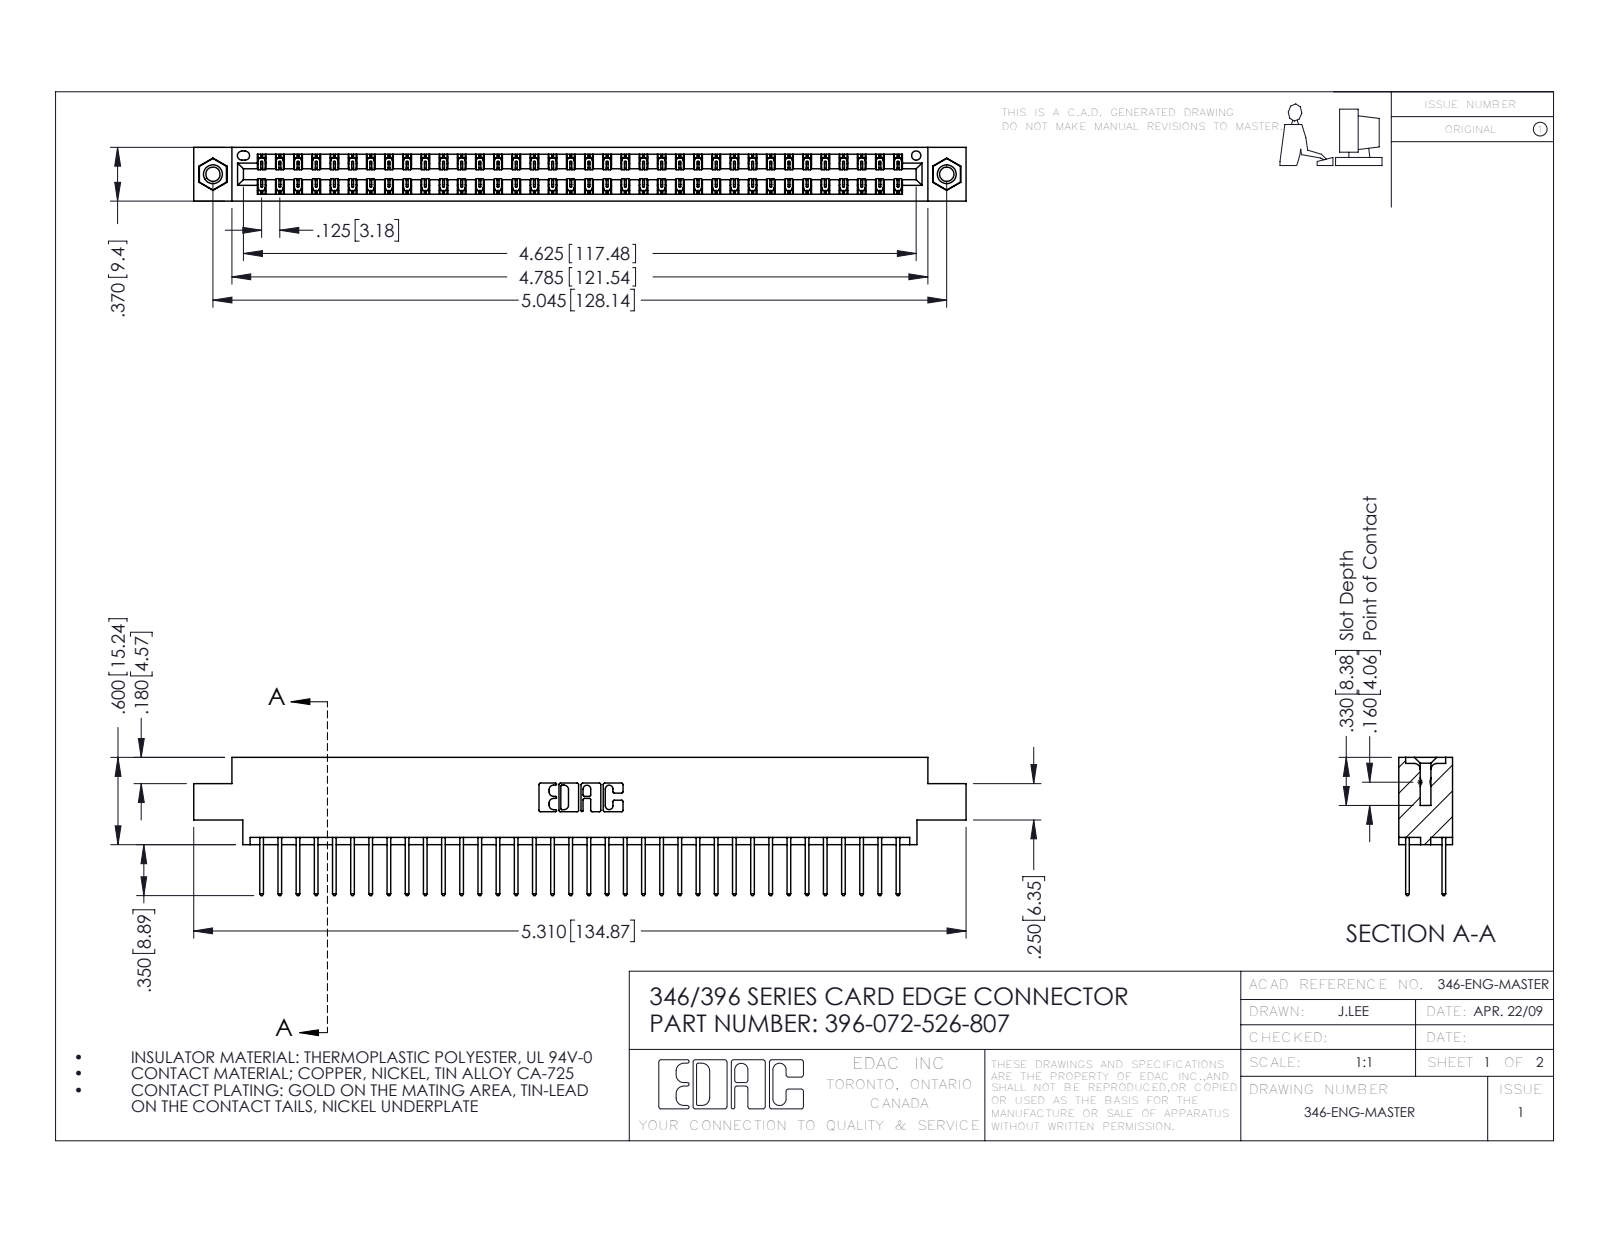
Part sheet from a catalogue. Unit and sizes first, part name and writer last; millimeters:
Units: millimetres
Overall size (bounding box): 134.9 × 24.1 × 9.4
Round holes (diameter × count): ⌀2.5 ×2, ⌀3.2 ×2, ⌀4 ×2, ⌀1.6 ×1
Round bosses / shafts (diameter × count): ⌀3.9 ×2
Partial cylindrical surfaces — rounded edges, fillets, slot ends (radius × count): R0.2 ×108, R0.3 ×72, R0.3 ×22, R0.2 ×6, R0.8 ×6, R0.7 ×3, R0.4 ×2, R0.6 ×2
Main face-to-face distances: 1.2, 8.2, 6.4, 9.4, 1.8, 7.6, 0.6, 7, 5.6, 3.8
Hole centre spacings: 6.2, 122.8, 128.1
Volume: 13 100 mm³ · Surface area: 18 590 mm²
Bodies: 75 solids, 3930 faces (2632 planar, 1282 cylindrical, 16 other)
Part name (STEP PRODUCT): 345-250-001_345-250-005-103; 396-072-526-807; 346 Part_0.170 Offset - 0.156 Dia-TI; 345-292-001_345-293-126
STEP written by: SolidWorks 2016 (CONFIG_CONTROL_DESIGN)
